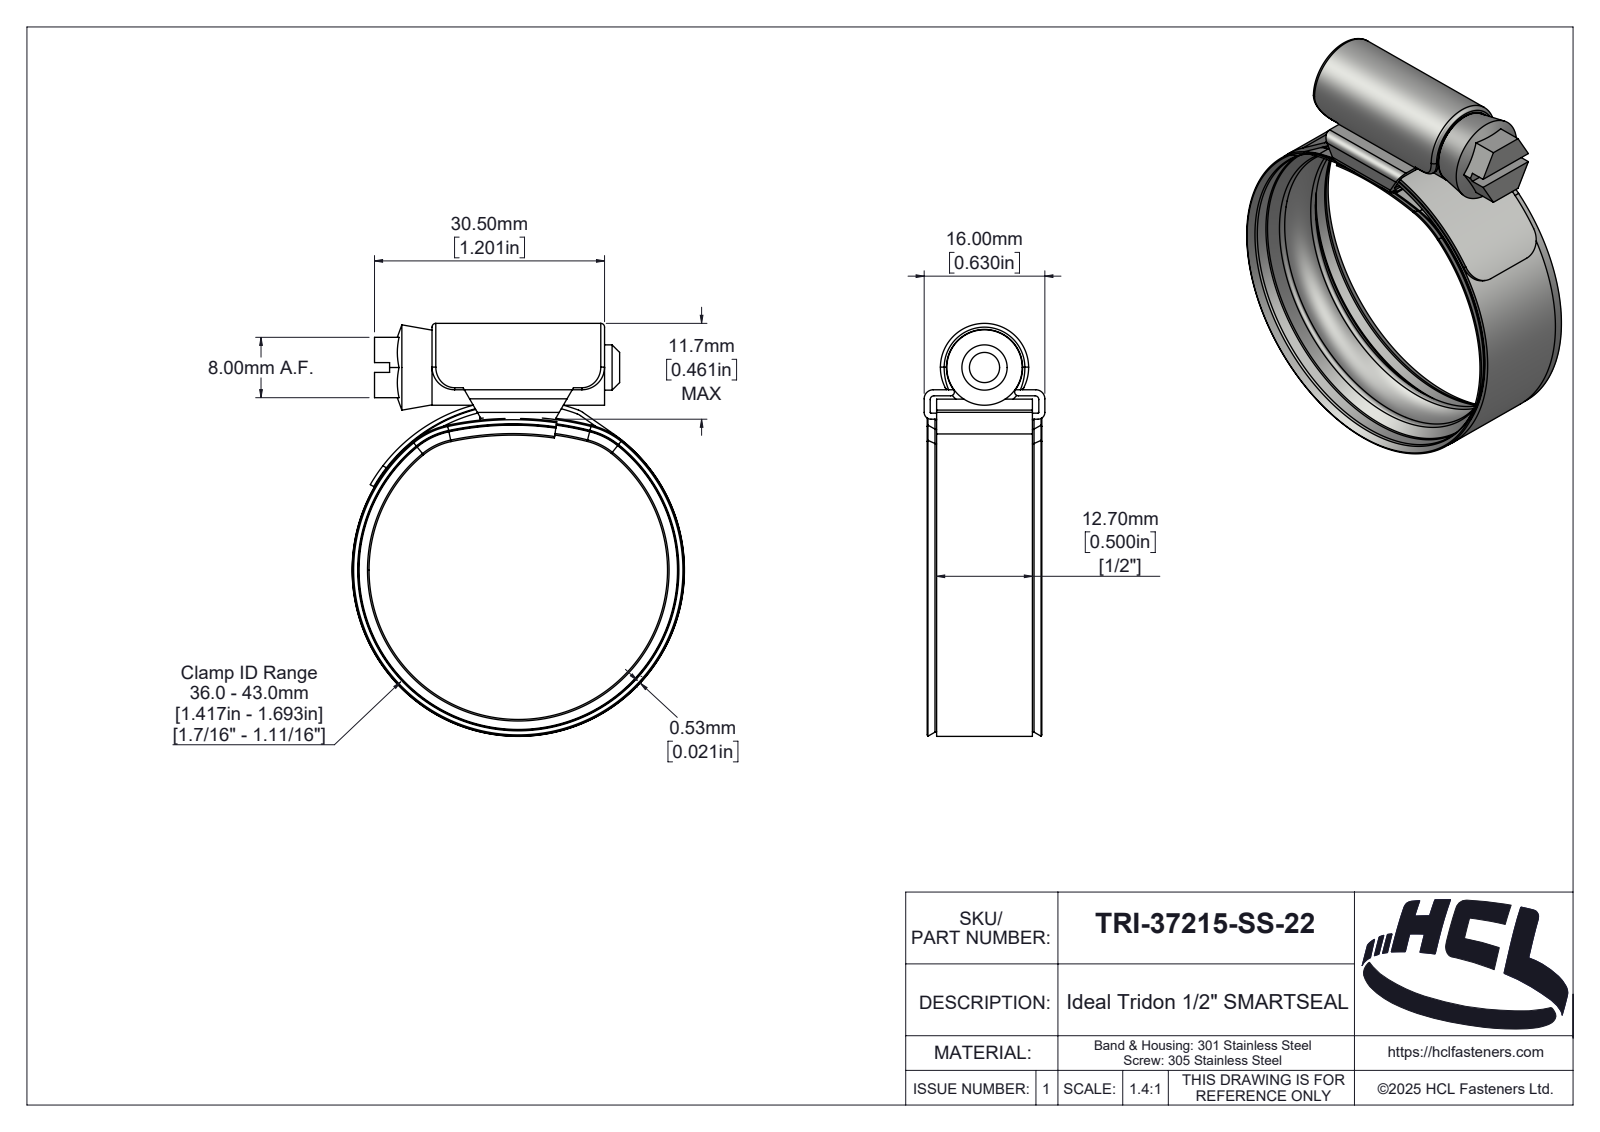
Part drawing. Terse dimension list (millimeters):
name: TRI-37215-SS-22
written by: SolidWorks 2025 (AUTOMOTIVE_DESIGN)
unit: mm
bodies: 4 solids, 418 faces (42 planar, 119 cylindrical, 257 other)
size: 54.73 × 44.06 × 16
volume: 4 609 mm³; area: 12 009 mm²
holes: 1× ⌀43
bosses: 1× ⌀44.06, 1× ⌀10, 1× ⌀6
rounds: 6× R0.5, 4× R3, 2× R0.1, 2× R0.9, 2× R1.2, 2× R9.9, 2× R10.1, 1× R0.46
face distances: 0.8, 3.1, 12.7, 2.3, 0.53, 30.5, 3.9, 1.65, 14.35, 15.2
